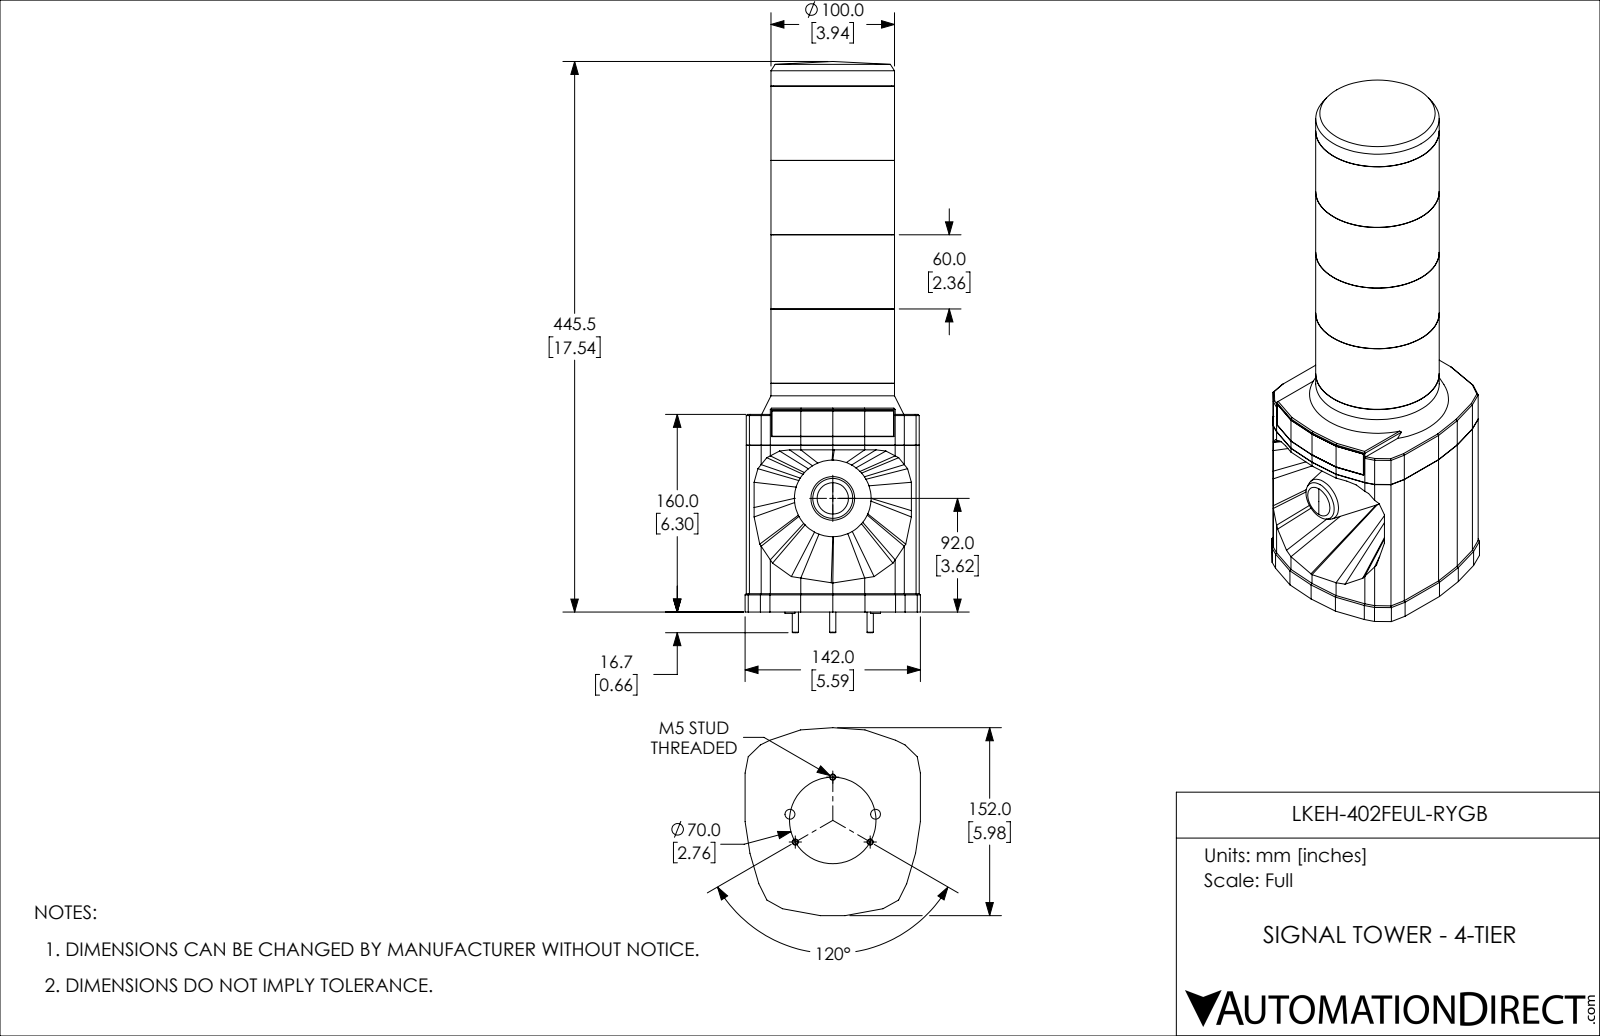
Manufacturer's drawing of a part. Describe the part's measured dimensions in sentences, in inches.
The part is named "LKEH-402FEUL-RYGB". Its 3-D file was written by "SolidWorks 2018 (AUTOMOTIVE_DESIGN)". It is 1 solid with 278 faces: 186 planar, 32 cylindrical and 60 other. Overall it measures 18.197 by 5.984 by 5.591 inches. Its volume is 289.4 cubic inches and its surface area 366.5 square inches. Round bosses or shafts: 3 of diameter 0.197, 2 of diameter 0.315, 1 of diameter 3.937, 1 of diameter 3.764. The main face-to-face distances are 0.039, 5.512, 6.299, 2.366, 4.732, 2.37, 2.362, 6.496, 0.197, 7.098.
